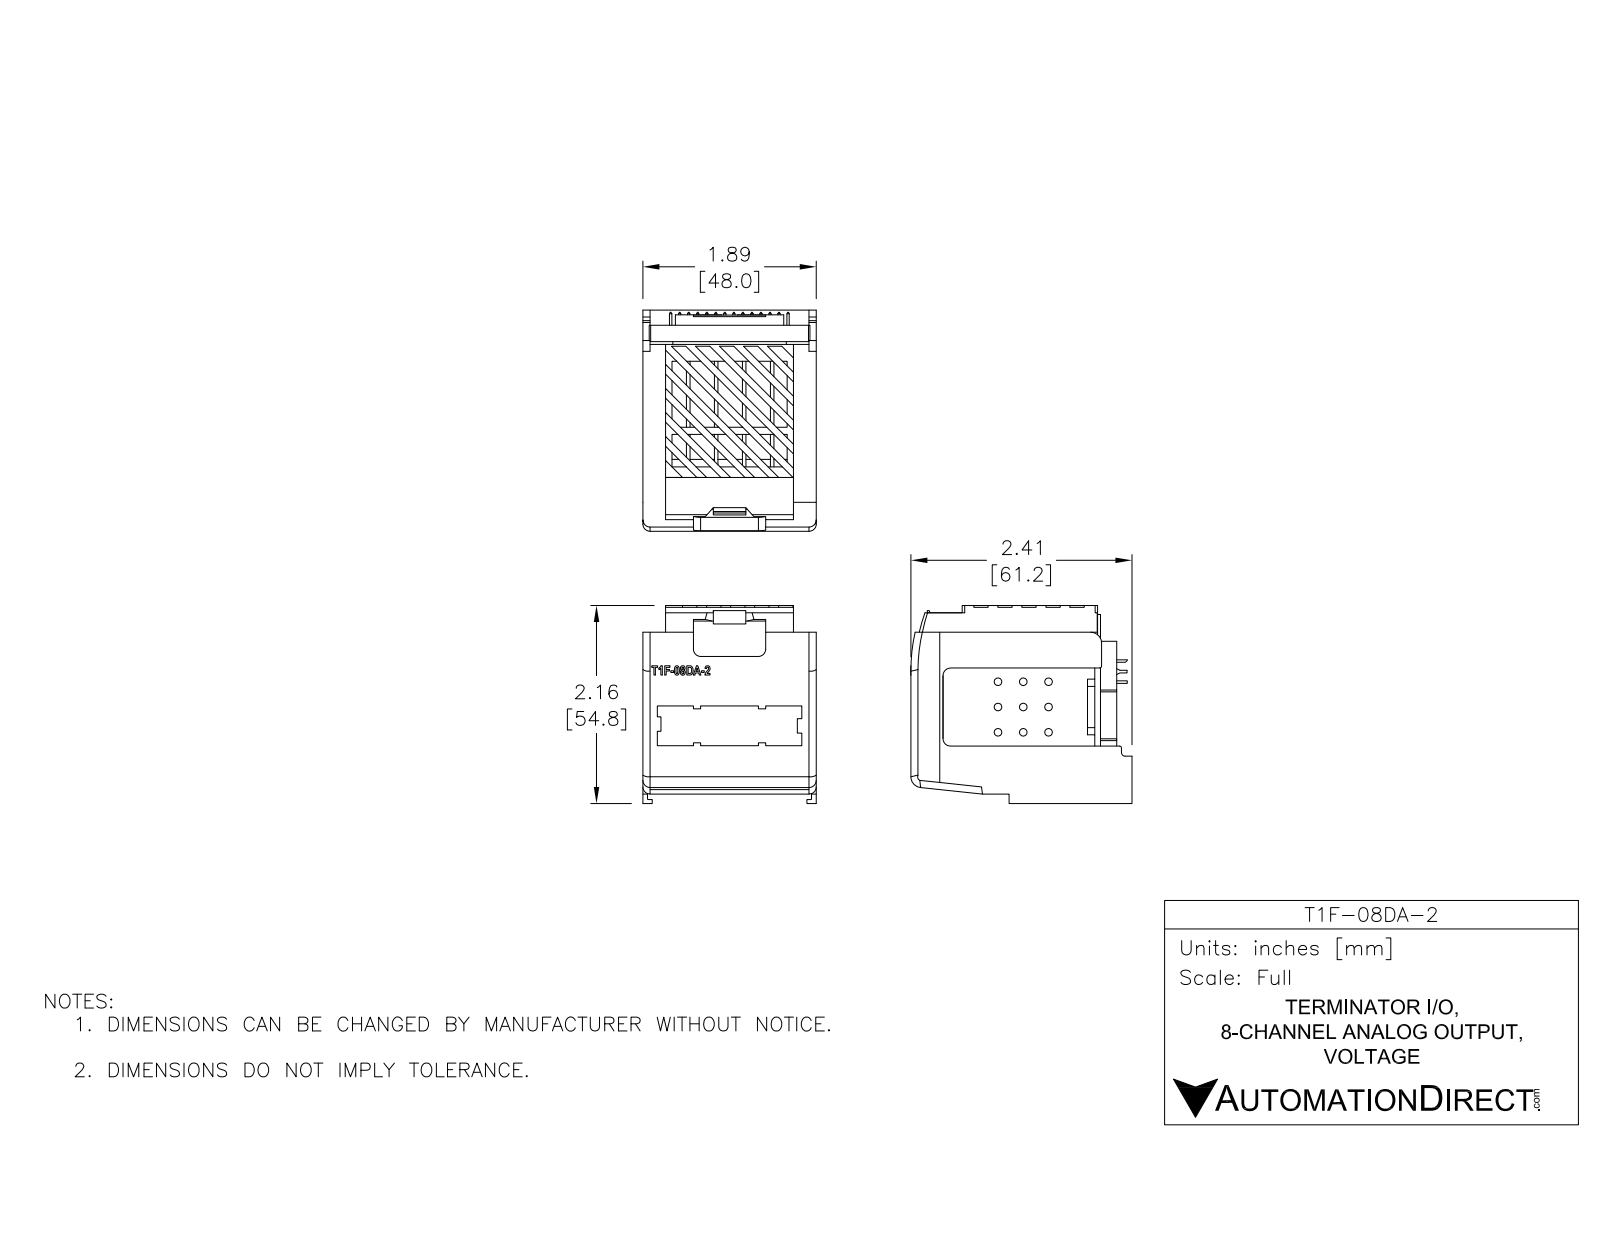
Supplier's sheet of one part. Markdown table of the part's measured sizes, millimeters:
| quantity | value |
| --- | --- |
| part name | T1F-08DA-2 |
| STEP written by | SolidWorks 2013 (AUTOMOTIVE_DESIGN) |
| units | millimeters |
| bodies | 1 solid, 563 faces (418 planar, 101 cylindrical, 44 other) |
| overall size | 65.1 × 61.36 × 47.6 |
| volume | 30 279 mm³ |
| surface area | 35 941 mm² |
| round holes (diameter × count) | 3 × 8 |
| round bosses / shafts (diameter × count) | 0.7 × 28 |
| partial cylindrical surfaces (radius × count) | 3.5 × 10, 1 × 5, 0.25 × 3, 0.55 × 3, 1.5 × 2, 8 × 1, 10 × 1, 18 × 1 |
| main face-to-face distances | 2, 45.6, 47.6, 43.6, 55.35, 49.9, 6.55, 39.05, 59.8, 9.9 |
| hole center spacings | 5.2, 10.4, 15.6, 20.8, 26, 31.2, 36.4 |
